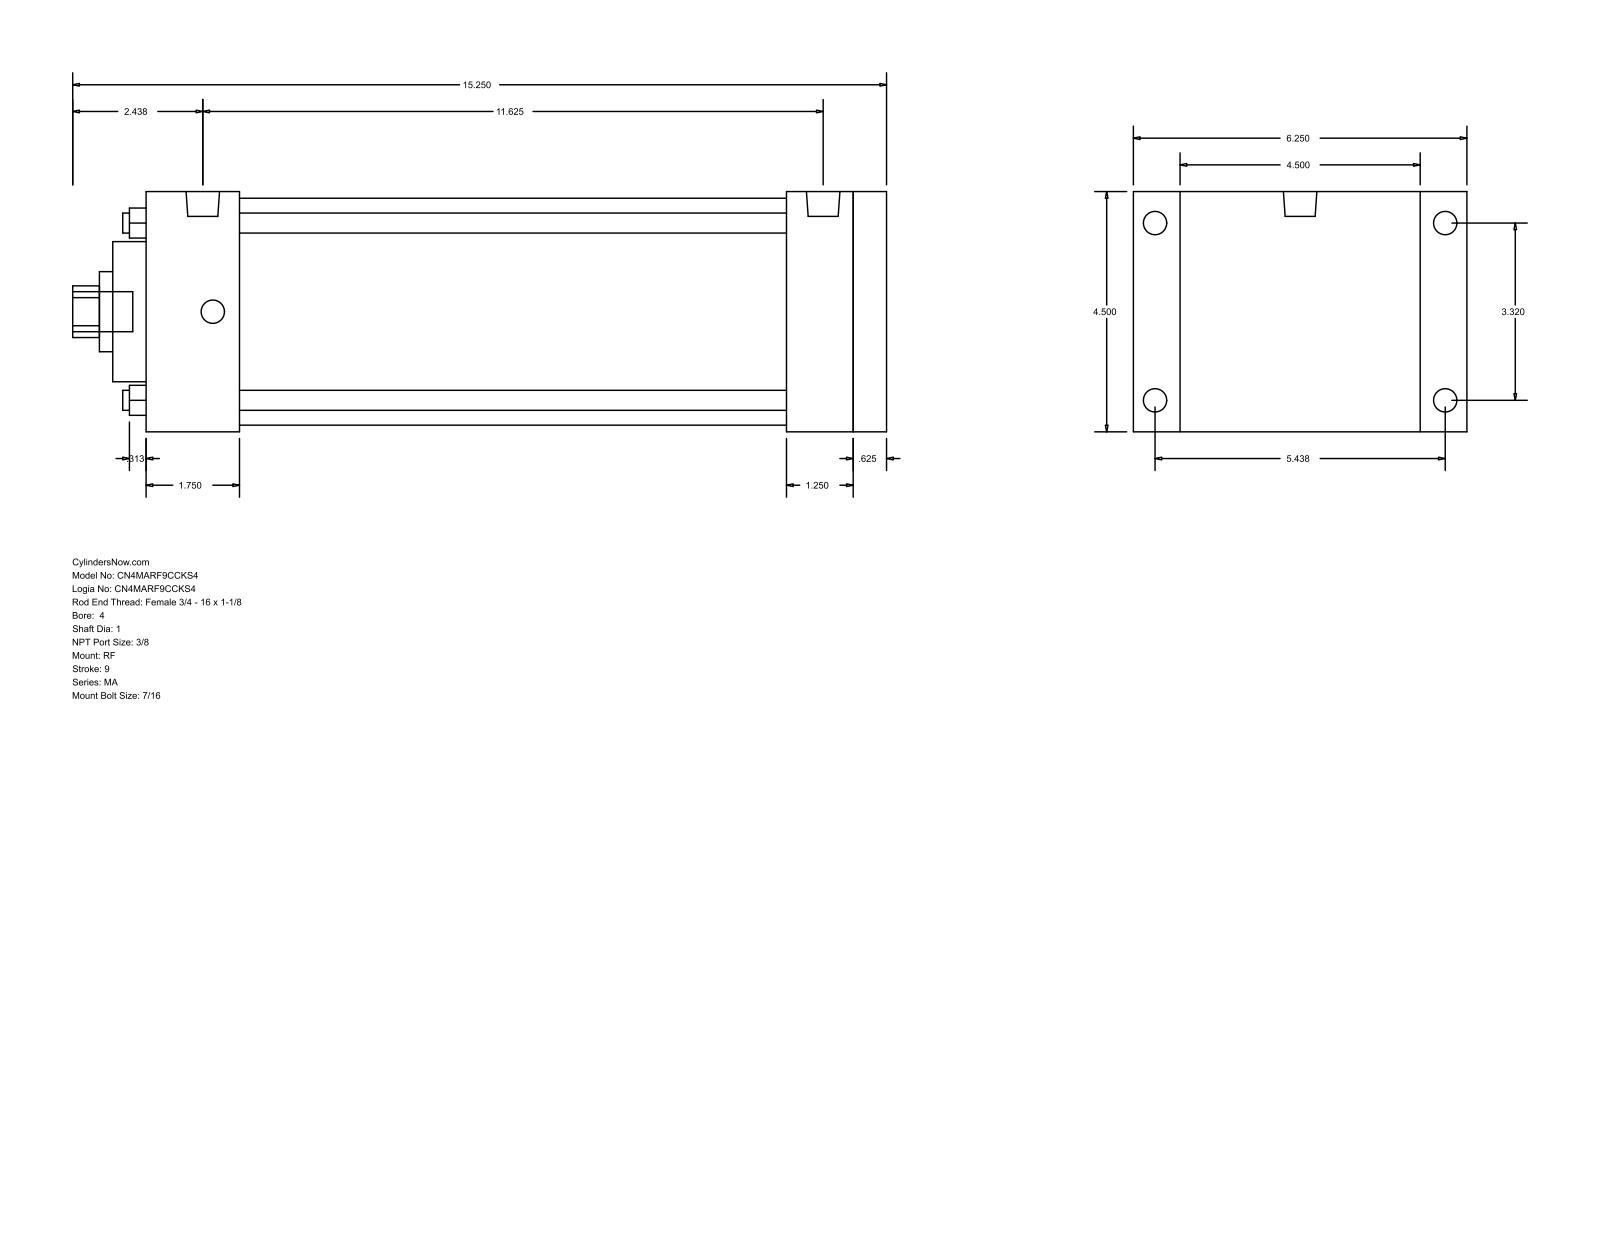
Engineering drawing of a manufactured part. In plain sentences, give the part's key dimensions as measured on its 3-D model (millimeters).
The part is named "MA_RF__0400_1". Its 3-D file was written by "GSSL Pune (CONFIG_CONTROL_DESIGN)". It is 0 solids with 94 faces: 65 planar, 29 cylindrical and 0 other. Overall it measures 387.35 by 158.75 by 114.3 millimeters. Round holes: 4 of diameter 9.53, 1 of diameter 25.4, 1 of diameter 38.1, 1 of diameter 66.67, 1 of diameter 107.95. Round bosses or shafts: 8 of diameter 11.11, 2 of diameter 15.93, 1 of diameter 19.05. Partial cylindrical surfaces (rounded edges, fillets, slot ends): 1 of radius 12.29. The main face-to-face distances are 114.3, 352.43, 15.87, 336.56, 22.23, 136.53, 304.81, 31.75, 47.62, 44.46. The hole center spacings are 59.62, 84.32, 119.25.
